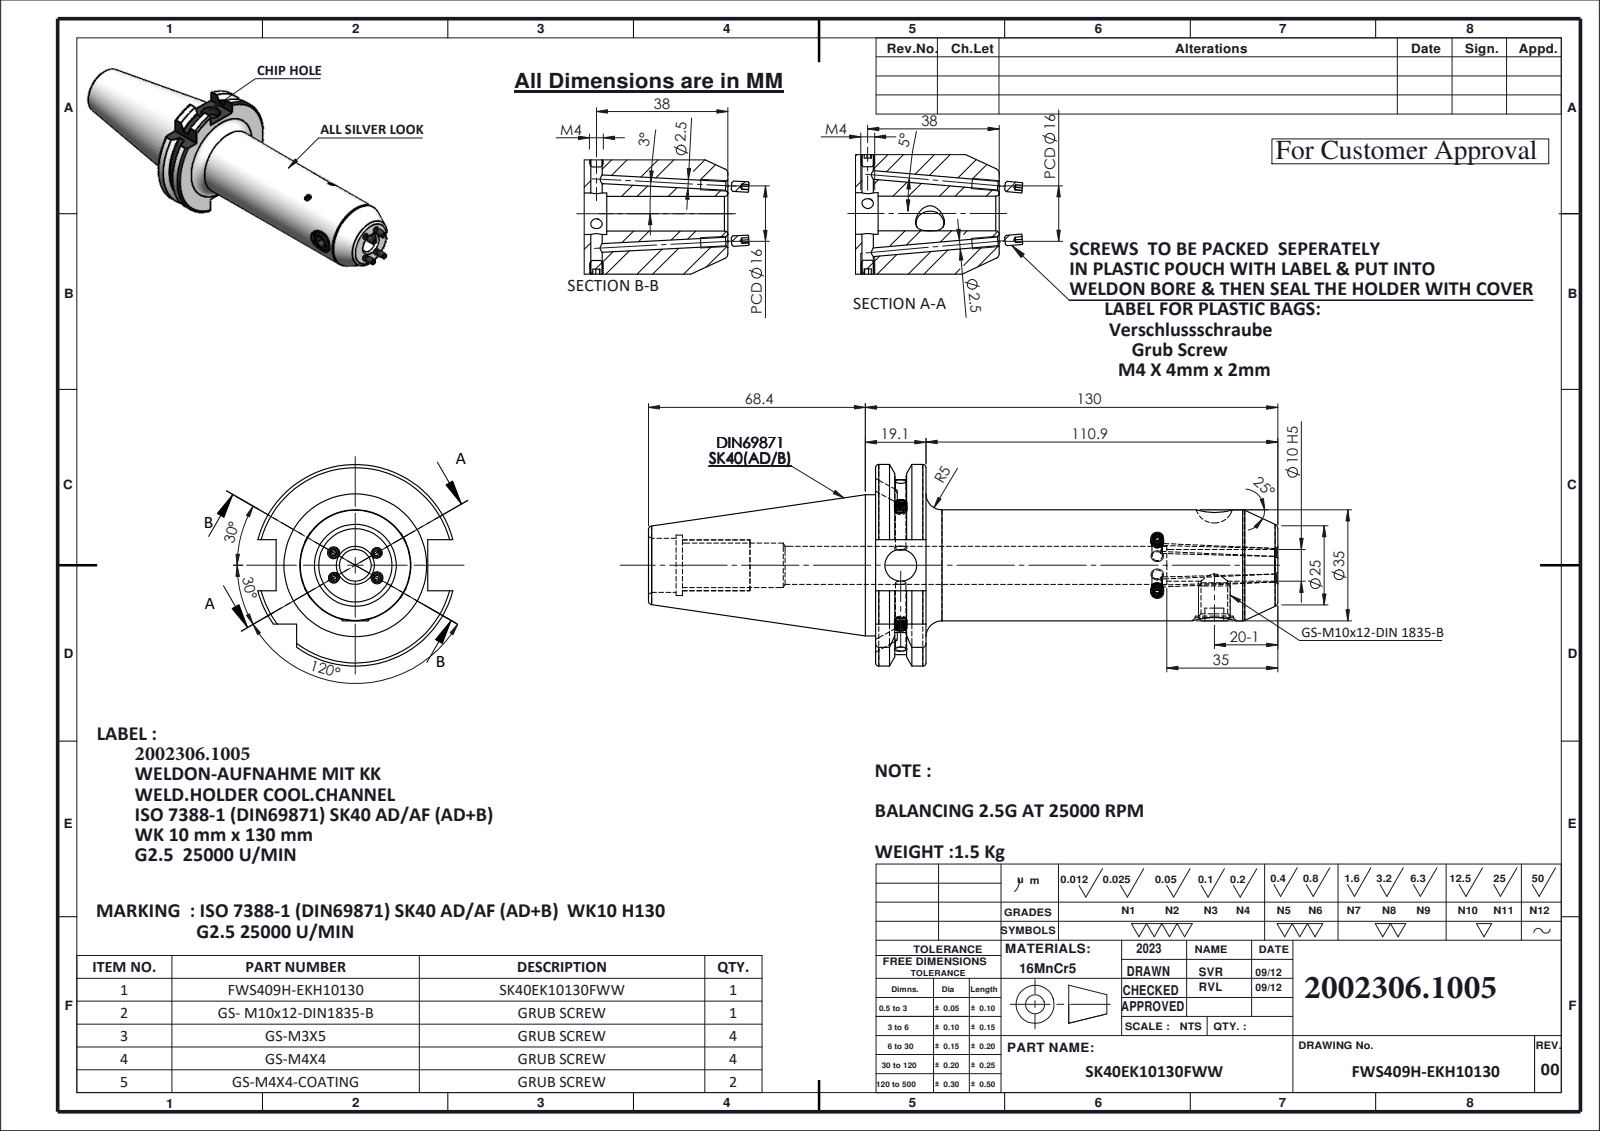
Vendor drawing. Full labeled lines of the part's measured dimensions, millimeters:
Part name (STEP PRODUCT): FWS409H-EKH10130; GS-M4X4_DIN 913 - M4 x 4-N; GS-M10X12-DIN1835-B; GS-M4X4-COATING_DIN 913 - M4 x 4-N (+2 more)
STEP written by: SolidWorks 2023 (CONFIG_CONTROL_DESIGN)
Units: millimetres
Bodies: 12 solids, 519 faces (149 planar, 122 cylindrical, 248 other)
Overall size (bounding box): 205.18 × 63.55 × 61.48
Volume: 192 389 mm³ · Surface area: 39 701 mm²
Round holes (diameter × count): ⌀2.5 ×4, ⌀3.3 ×3, ⌀10 ×2, ⌀12 ×2, ⌀8.4 ×1, ⌀14 ×1, ⌀17 ×1, ⌀19 ×1
Round bosses / shafts (diameter × count): ⌀4 ×4, ⌀3 ×4, ⌀44.45 ×1, ⌀35 ×1, ⌀10 ×1
Partial cylindrical surfaces — rounded edges, fillets, slot ends (radius × count): R28.12 ×1, R31.77 ×1
Main face-to-face distances: 15.9, 126.8, 110.9, 16.1, 47.8, 71.6, 87.5, 198.4, 10.7, 60.9
